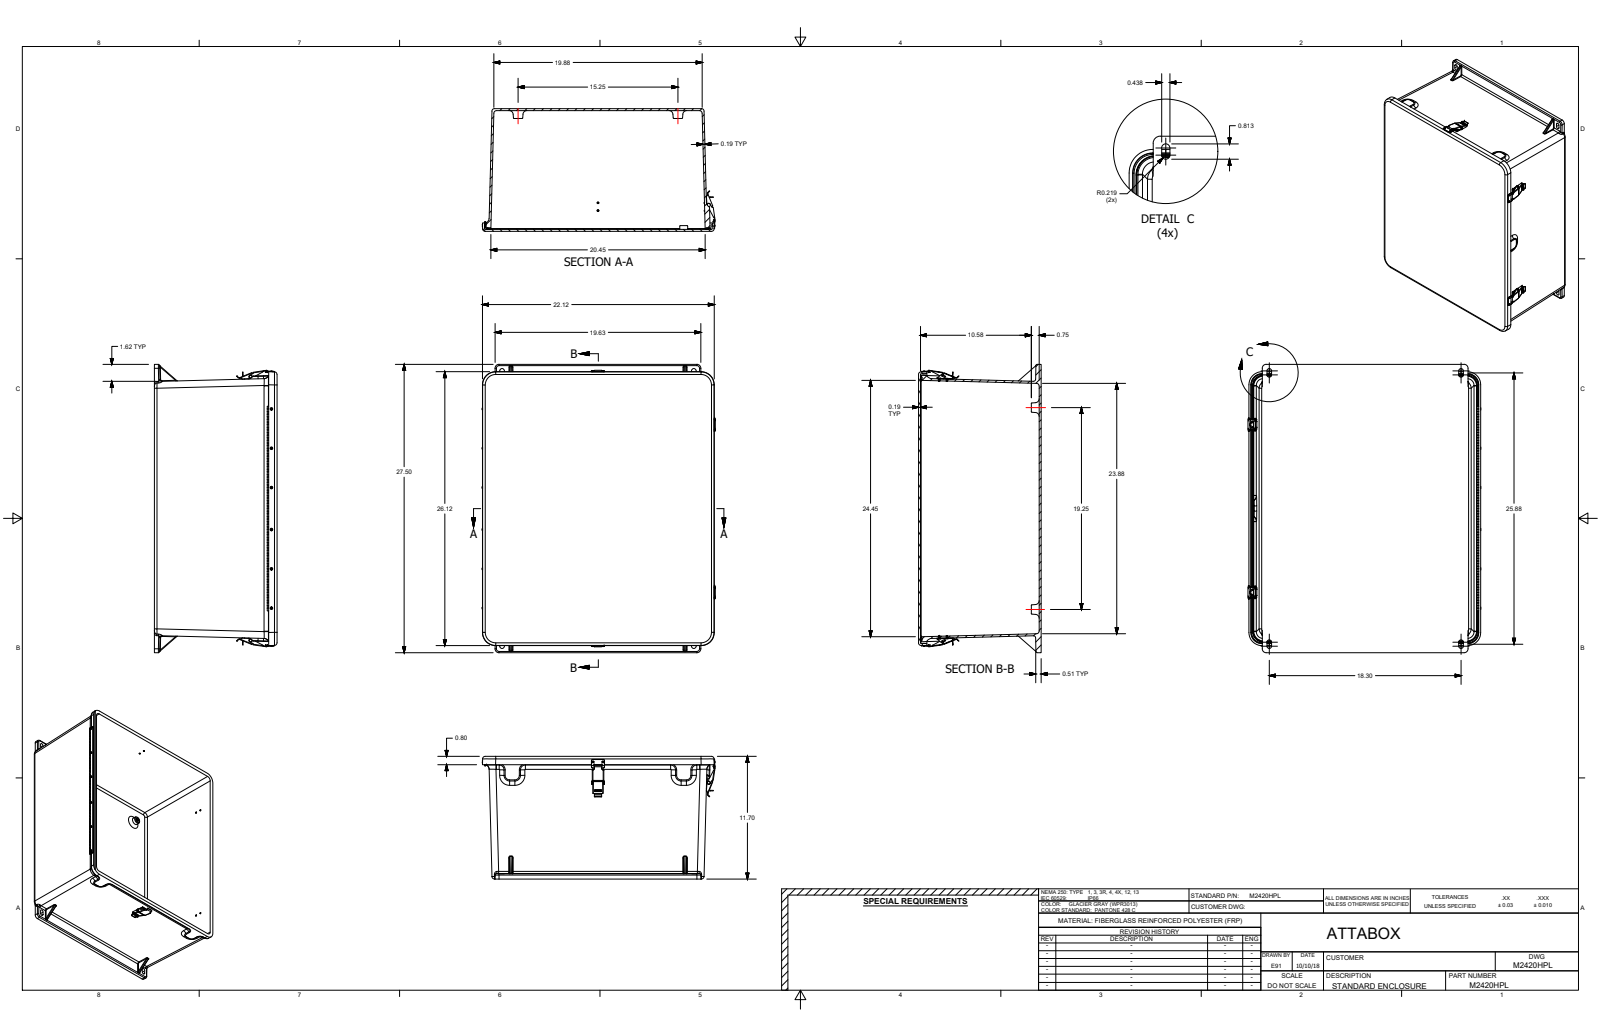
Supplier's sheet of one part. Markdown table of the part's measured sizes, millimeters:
| quantity | value |
| --- | --- |
| part name | M2420HPL |
| STEP written by | SolidWorks 2018 (AUTOMOTIVE_DESIGN) |
| units | millimeters |
| bodies | 62 solids, 2139 faces (803 planar, 878 cylindrical, 458 other) |
| overall size | 698.5 × 564.5 × 297.2 |
| volume | 7 941 000 mm³ |
| surface area | 2 993 000 mm² |
| round holes (diameter × count) | 2.6 × 28, 3.5 × 24, 3.3 × 12, 3.3 × 8, 3.6 × 8, 3.4 × 6, 5.2 × 4, 8 × 4, 9.5 × 4, 3.4 × 3, 7.9 × 2, 2.2 × 1 |
| round bosses / shafts (diameter × count) | 3.2 × 17, 3.2 × 11, 9.9 × 4, 7.6 × 3, 4.3 × 3, 3 × 3, 3.9 × 1, 2.2 × 1 |
| partial cylindrical surfaces (radius × count) | 0.1 × 72, 0.4 × 44, 3.2 × 40, 0.5 × 34, 1.1 × 32, 0.8 × 24, 1.5 × 22, 1.6 × 20 |
| main face-to-face distances | 4.8, 292.4, 297.2, 287.7, 4.8, 12, 290.5, 285.8, 1.9, 6.7 |
| hole center spacings | 95.3, 190.5, 23.8, 406.4, 279.4, 292.1, 184.2, 196.9 |
